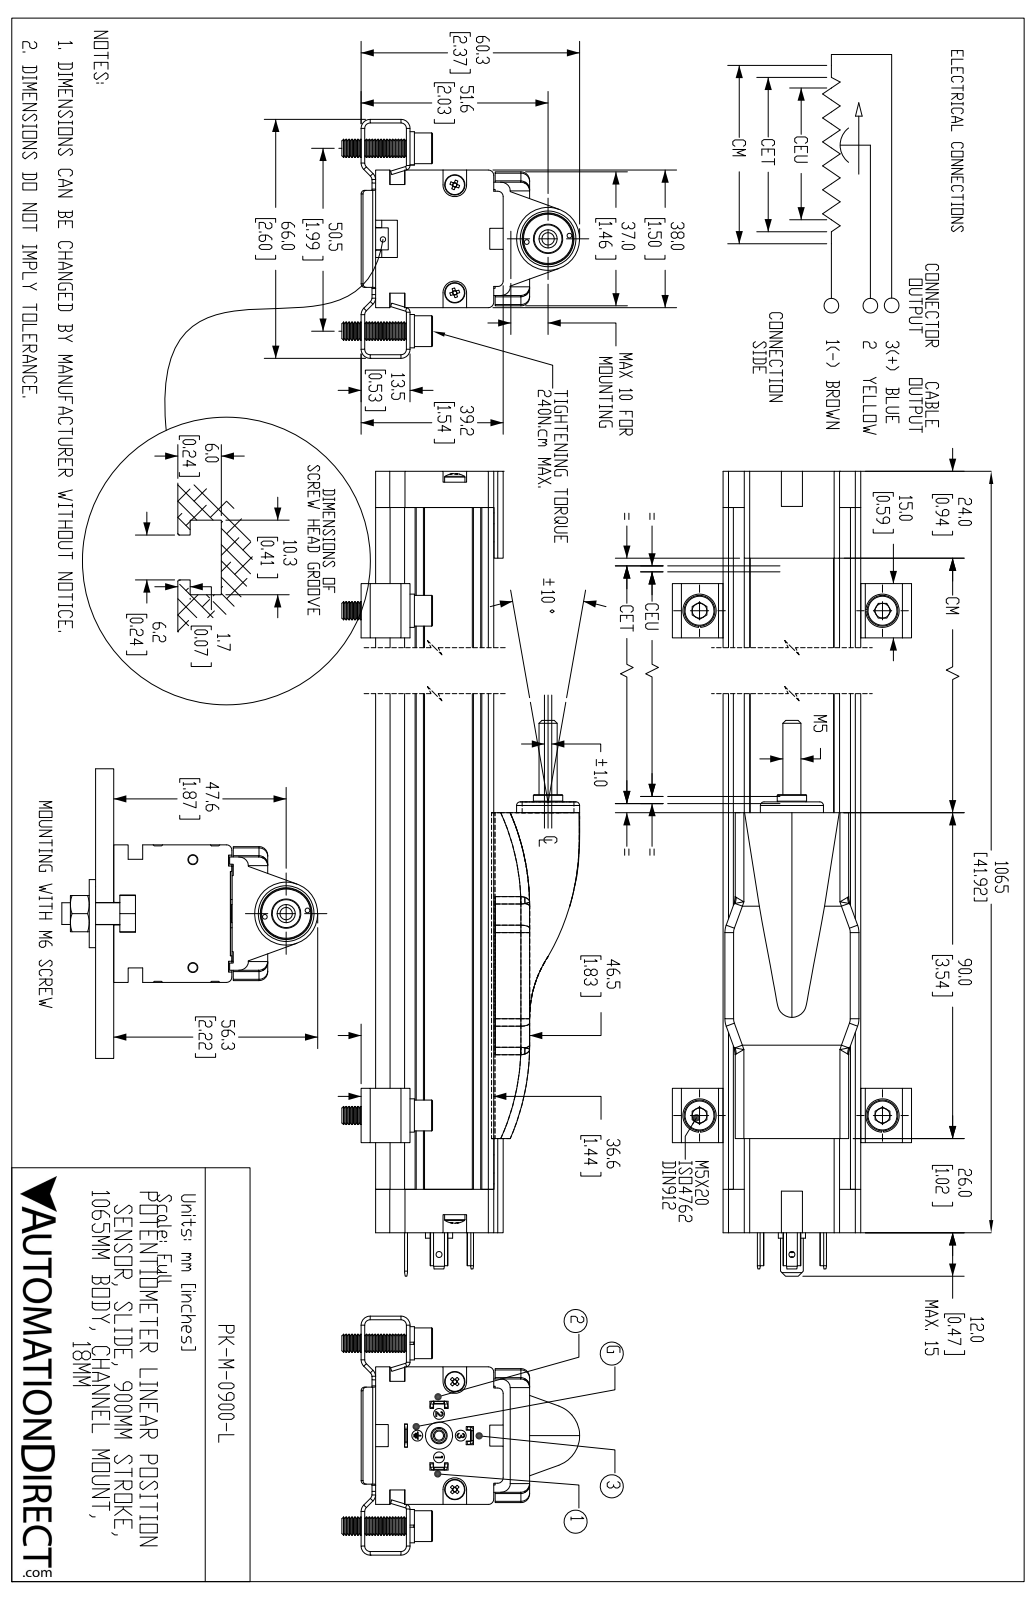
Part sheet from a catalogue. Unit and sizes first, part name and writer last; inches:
Units: inches
Overall size (bounding box): 42.402 × 2.598 × 2.583
Round holes (diameter × count): ⌀0.118 ×5, ⌀0.201 ×4, ⌀0.051 ×2, ⌀0.059 ×2, ⌀0.065 ×2, ⌀0.102 ×2, ⌀0.108 ×2, ⌀0.13 ×2, ⌀0.209 ×2, ⌀0.063 ×1, ⌀0.098 ×1, ⌀0.157 ×1
Round bosses / shafts (diameter × count): ⌀0.197 ×7, ⌀0.362 ×4, ⌀0.335 ×4, ⌀0.22 ×2, ⌀0.118 ×2, ⌀0.098 ×2, ⌀0.685 ×1, ⌀0.551 ×1
Partial cylindrical surfaces — rounded edges, fillets, slot ends (radius × count): R0.039 ×28, R0.059 ×12, R0.098 ×8, R0.104 ×8, R0.236 ×8, R0.033 ×6, R0.094 ×6, R0.024 ×4
Main face-to-face distances: 1.268, 0.157, 1.272, 1.496, 0.079, 1.035, 0.236, 0.315, 1.031, 0.02
Hole centre spacings: 0.236, 0.334, 0.234, 0.39, 0.472, 0.484, 0.539, 0.59
Volume: 75.72 in³ · Surface area: 454.4 in²
Bodies: 27 solids, 1761 faces (785 planar, 384 cylindrical, 592 other)
Part name (STEP PRODUCT): PK-M-0900-L
STEP written by: SolidWorks 2019 (AUTOMOTIVE_DESIGN)
